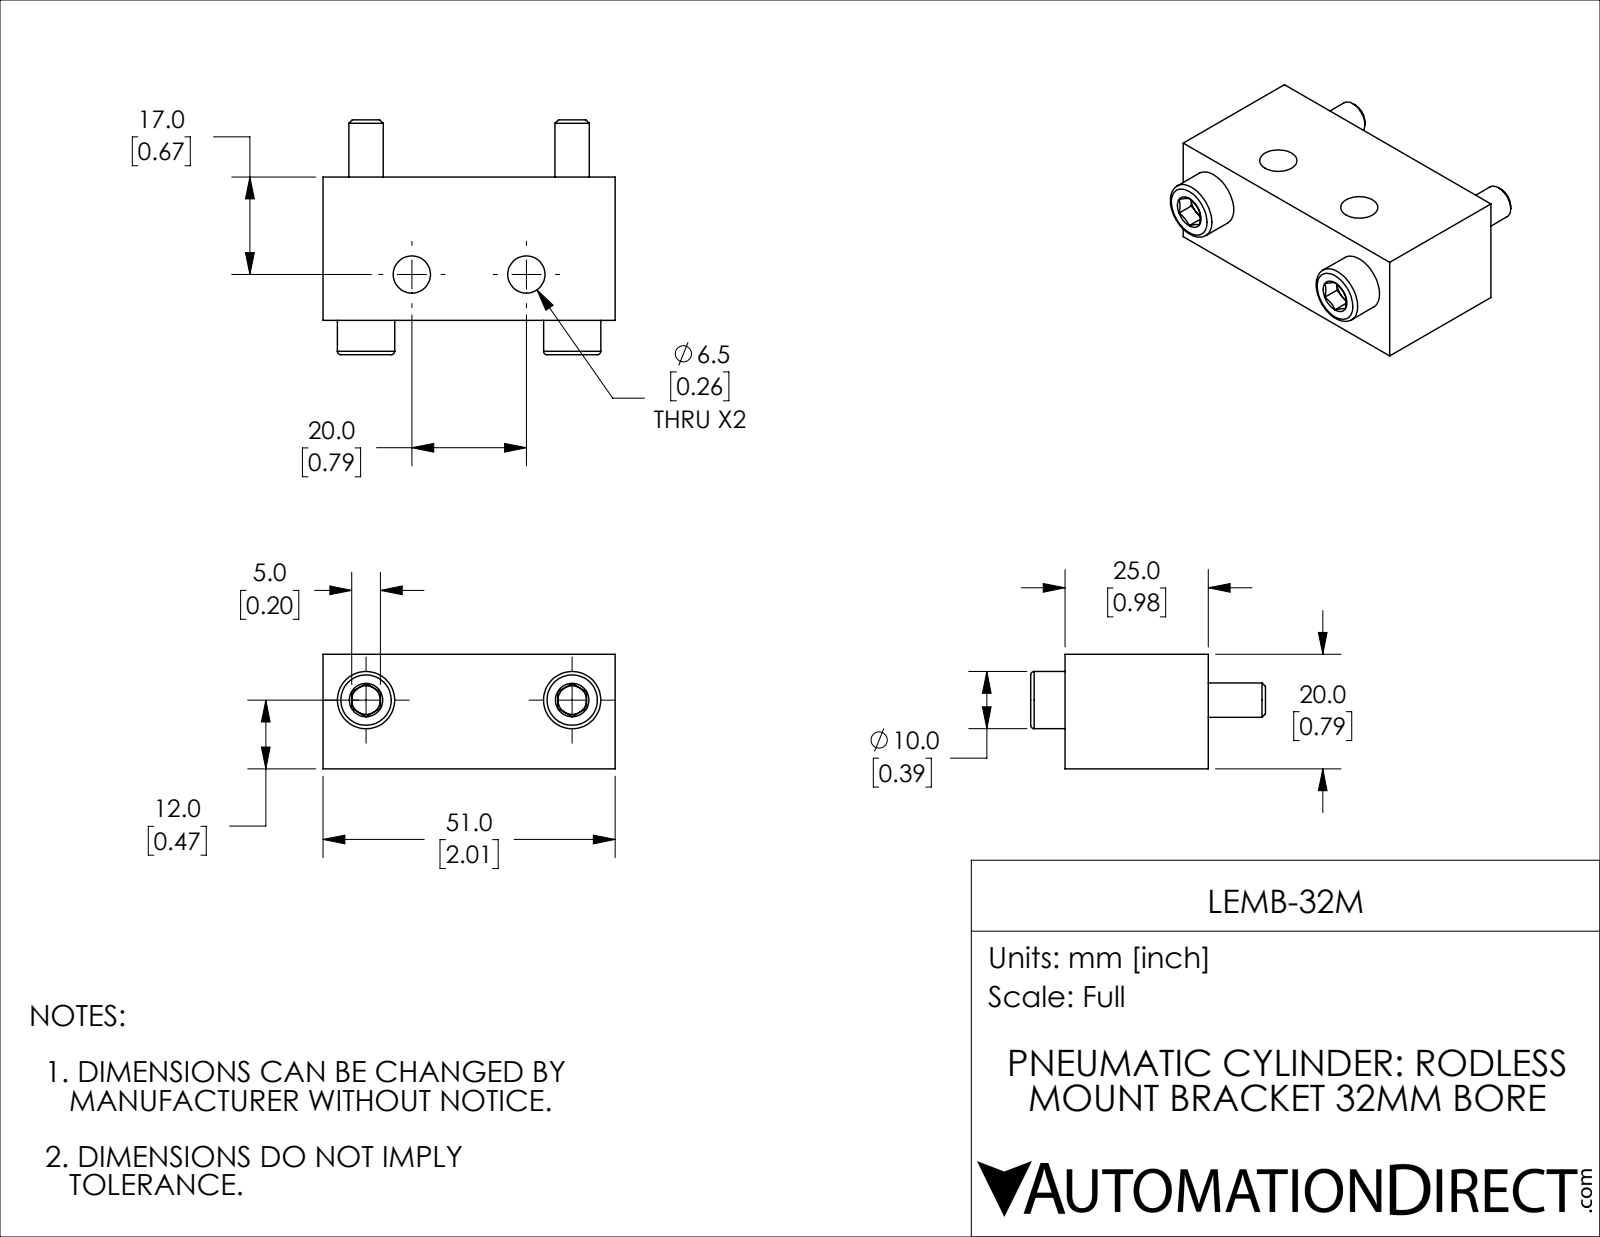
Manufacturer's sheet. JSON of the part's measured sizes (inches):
{"part_name": "LEMB-32M", "step_written_by": "SolidWorks 2019 (CONFIG_CONTROL_DESIGN)", "units": "inches", "bodies": {"solids": 3, "faces": 80, "planar": 36, "cylindrical": 16, "other": 28}, "overall_size": [2.008, 1.614, 0.787], "volume_in3": 1.557, "surface_area_in2": 14.23, "round_holes": [[0.236, 2], [0.256, 2]], "round_bosses_or_shafts": [[0.394, 2]], "face_to_face_distances": [0.787, 0.984, 2.008, 1.22, 0.236, 0.197, 1.614, 0.394, 1.378, 0.709], "hole_center_spacings": [0.787, 1.417]}
